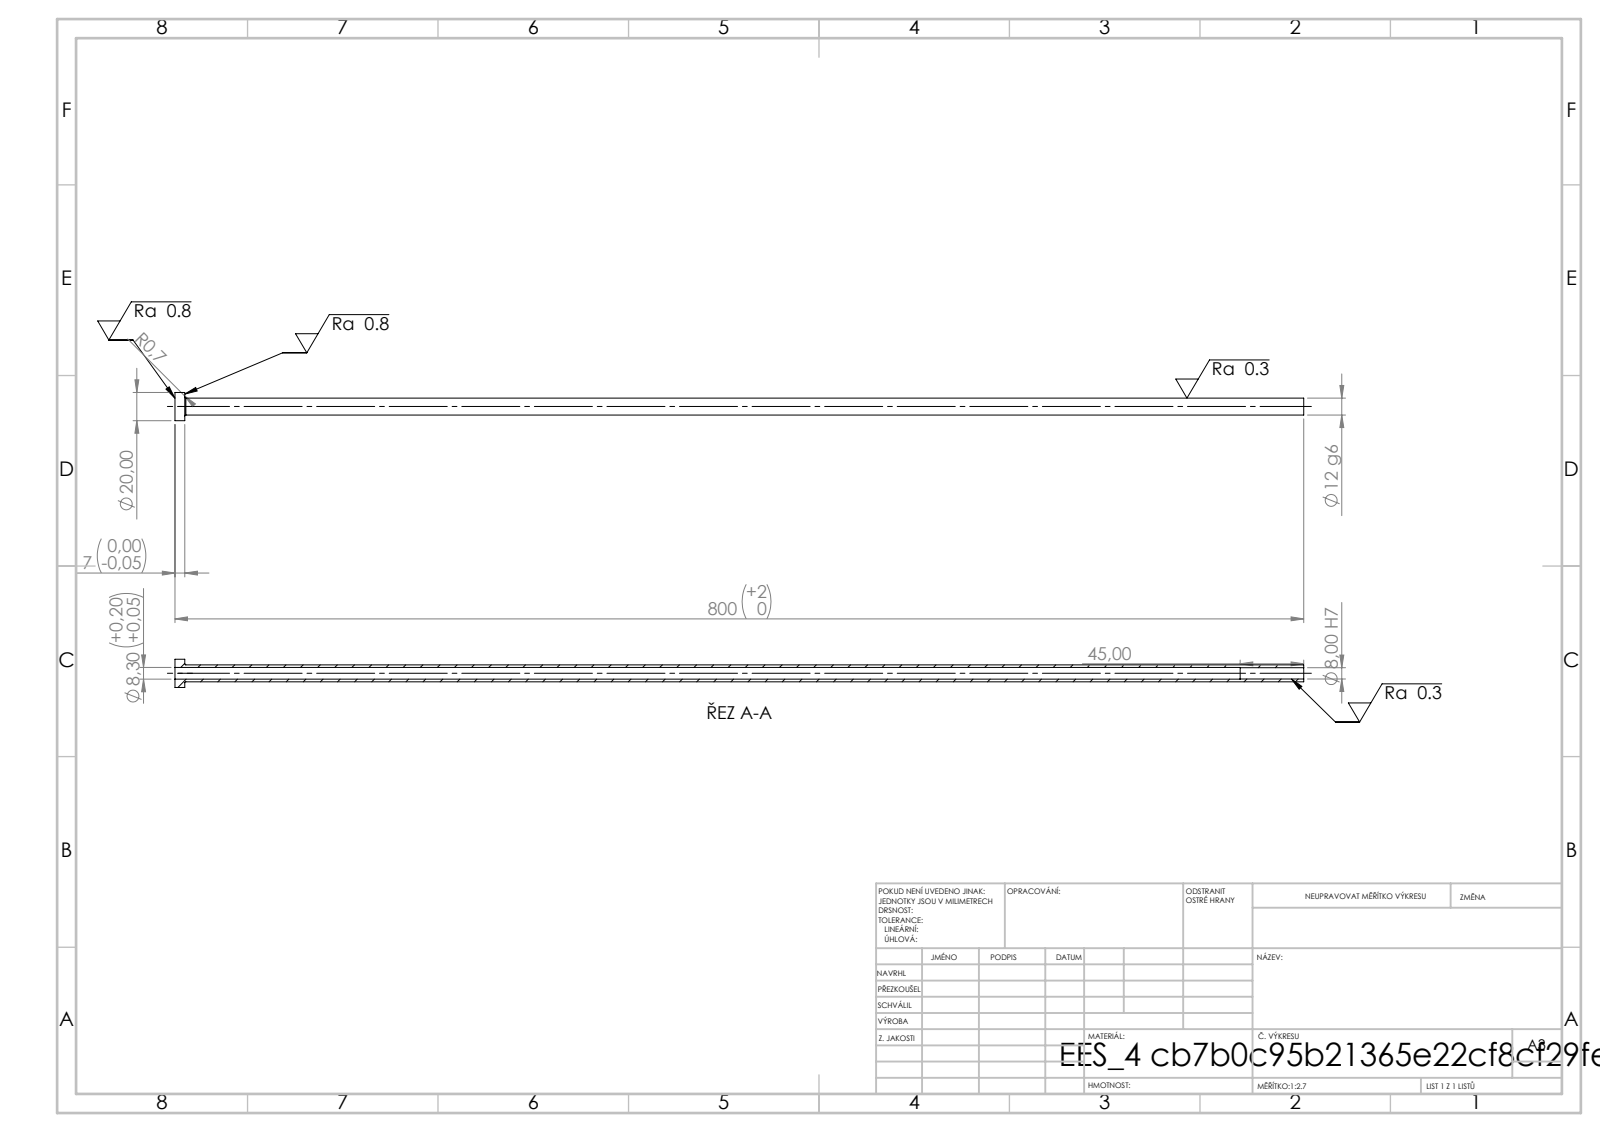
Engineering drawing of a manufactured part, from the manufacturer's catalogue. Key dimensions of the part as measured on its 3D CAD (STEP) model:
STEP written by: SolidWorks 2019 (CONFIG_CONTROL_DESIGN)
Units: millimetres
Bodies: 1 solid, 14 faces (4 planar, 8 cylindrical, 2 other)
Overall size (bounding box): 800 × 20 × 20
Volume: 48 777 mm³ · Surface area: 51 670 mm²
Round holes (diameter × count): ⌀8 ×1, ⌀8.3 ×1
Round bosses / shafts (diameter × count): ⌀20 ×1, ⌀12 ×1
Main face-to-face distances: 7, 800, 793, 755, 748, 45
